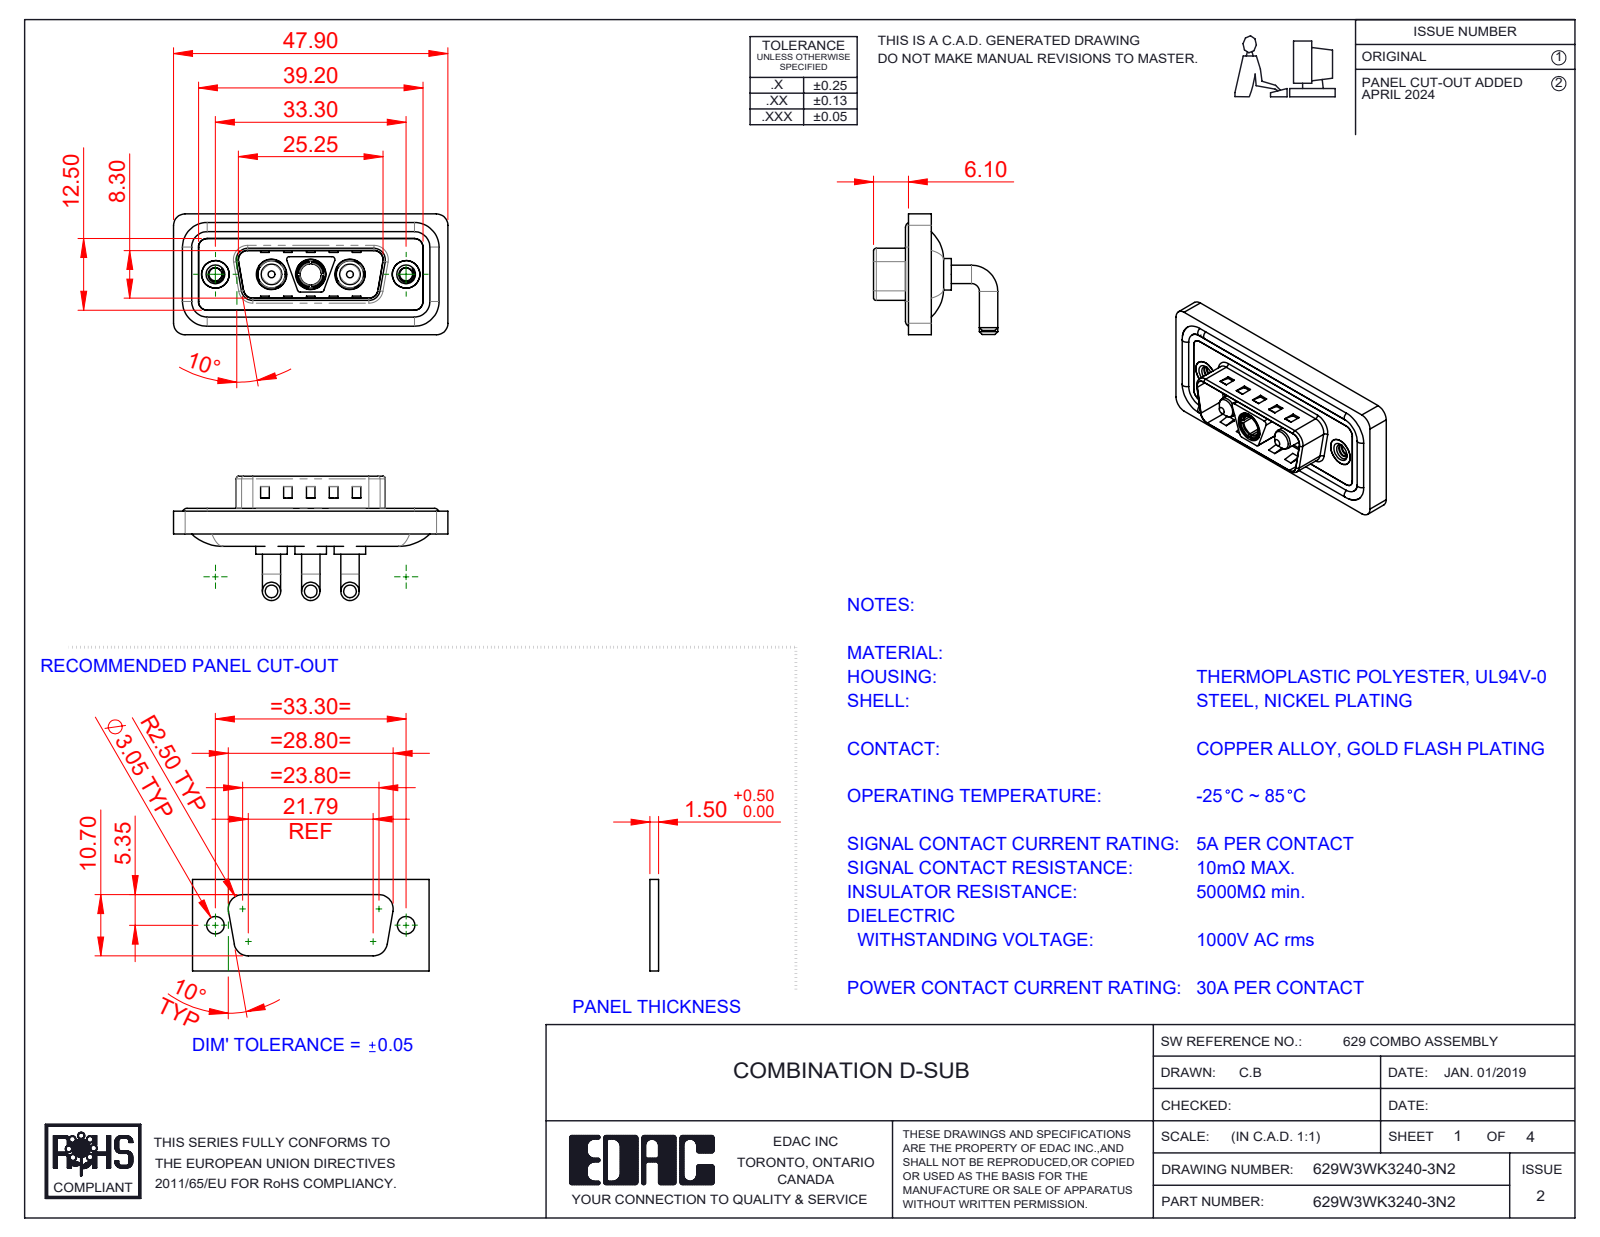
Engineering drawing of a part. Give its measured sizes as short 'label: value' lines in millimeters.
name: 629Combo Housing_3WK3; 629Combo Shell Rear_15 Contacts; Power Socket_30A RA; 629Combo Waterproof Housing_15 Contacts (+4 more)
written by: SolidWorks 2023 (CONFIG_CONTROL_DESIGN)
unit: mm
bodies: 13 solids, 621 faces (231 planar, 256 cylindrical, 134 other)
size: 47.9 × 21.7 × 21.1
volume: 5 981 mm³; area: 9 472 mm²
holes: 3× ⌀4.85, 3× ⌀5.3, 2× ⌀2.26, 2× ⌀4, 2× ⌀4.8, 2× ⌀5, 1× ⌀3.7
bosses: 6× ⌀3.2, 4× ⌀1.6, 3× ⌀5.5, 3× ⌀5.2, 3× ⌀4.75, 3× ⌀3.75, 2× ⌀4.9, 2× ⌀3.6
rounds: 20× R2, 18× R1.5, 12× R0.5, 8× R1.6, 4× R0.25, 4× R0.6, 4× R0.65, 4× R0.9
face distances: 0.4, 2.9, 0.8, 1.1, 2.1, 1.6, 3.1, 2.5, 4.5, 3.7
hole spacings: 6.85, 9.8, 16.65, 23.5, 13.7, 33.3
